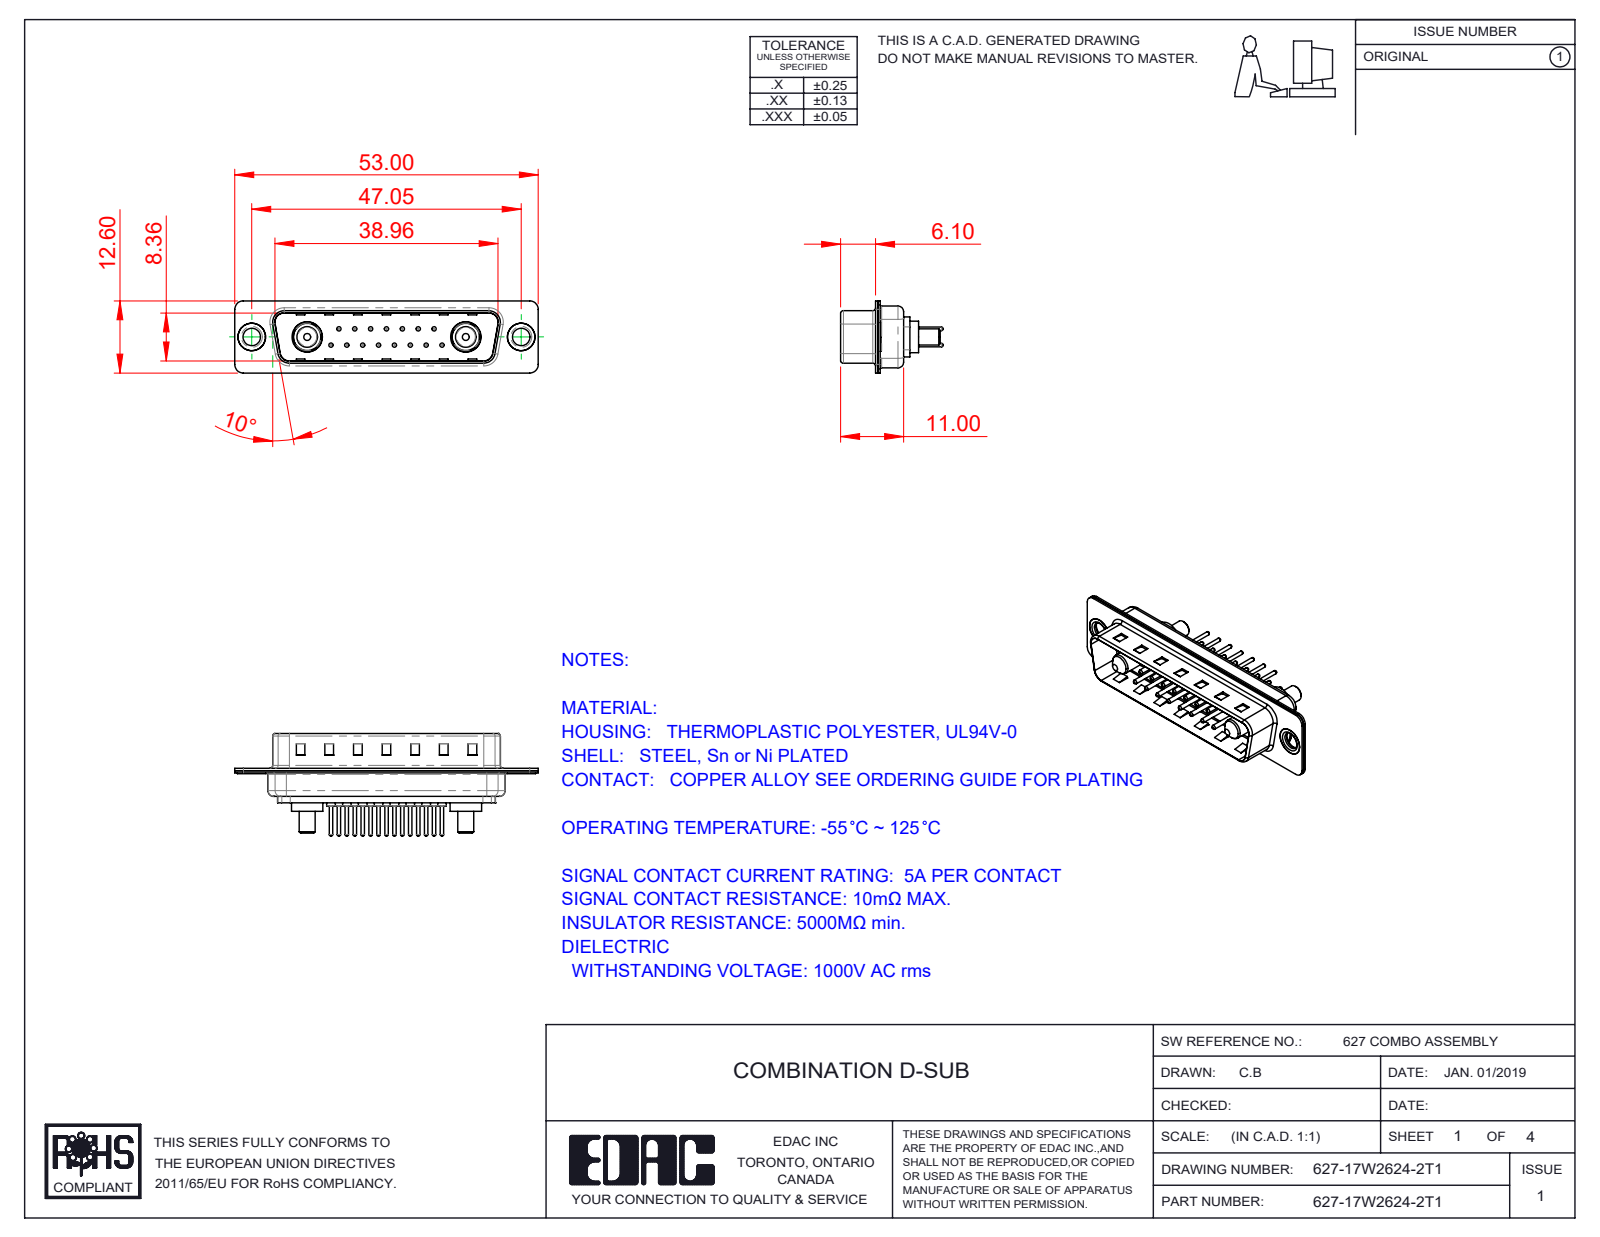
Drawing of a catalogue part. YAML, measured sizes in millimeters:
part_name: "627Combo Thru Hole Rivet; 627-17W2624-2T1; 627Combo Shell Front_25 Contacts; 627Combo Housing_17W2 (+4 more)"
step_written_by: "SolidWorks 2016 (CONFIG_CONTROL_DESIGN)"
units: millimeters
bodies: {solids: 24, faces: 985, planar: 296, cylindrical: 369, other: 320}
overall_size: [53, 17.9, 12.6]
volume: 2778
surface_area: 6643
round_holes:
  - {diameter: 0.75, count: 15}
  - {diameter: 1.6, count: 15}
  - {diameter: 2, count: 15}
  - {diameter: 3.05, count: 2}
  - {diameter: 4, count: 2}
  - {diameter: 4.8, count: 2}
  - {diameter: 4.85, count: 2}
  - {diameter: 5.3, count: 2}
round_bosses_or_shafts:
  - {diameter: 1.5, count: 15}
  - {diameter: 0.6, count: 15}
  - {diameter: 5.5, count: 2}
  - {diameter: 5.2, count: 2}
  - {diameter: 5, count: 2}
  - {diameter: 4.9, count: 2}
  - {diameter: 4.75, count: 2}
  - {diameter: 3.75, count: 2}
partial_cylinders:
  - {radius: 1.5, count: 16}
  - {radius: 2, count: 12}
  - {radius: 0.5, count: 8}
  - {radius: 1.6, count: 8}
  - {radius: 0.25, count: 4}
  - {radius: 0.6, count: 4}
  - {radius: 0.65, count: 4}
  - {radius: 0.9, count: 4}
face_to_face_distances: [0.4, 0.82, 9.58, 8.76, 1.5, 5.6, 5.2, 0.8, 1.22, 9.98]
hole_center_spacings: [3.16, 2.77, 5.54, 8.31, 5.04, 7.49, 11.08, 5.03]
